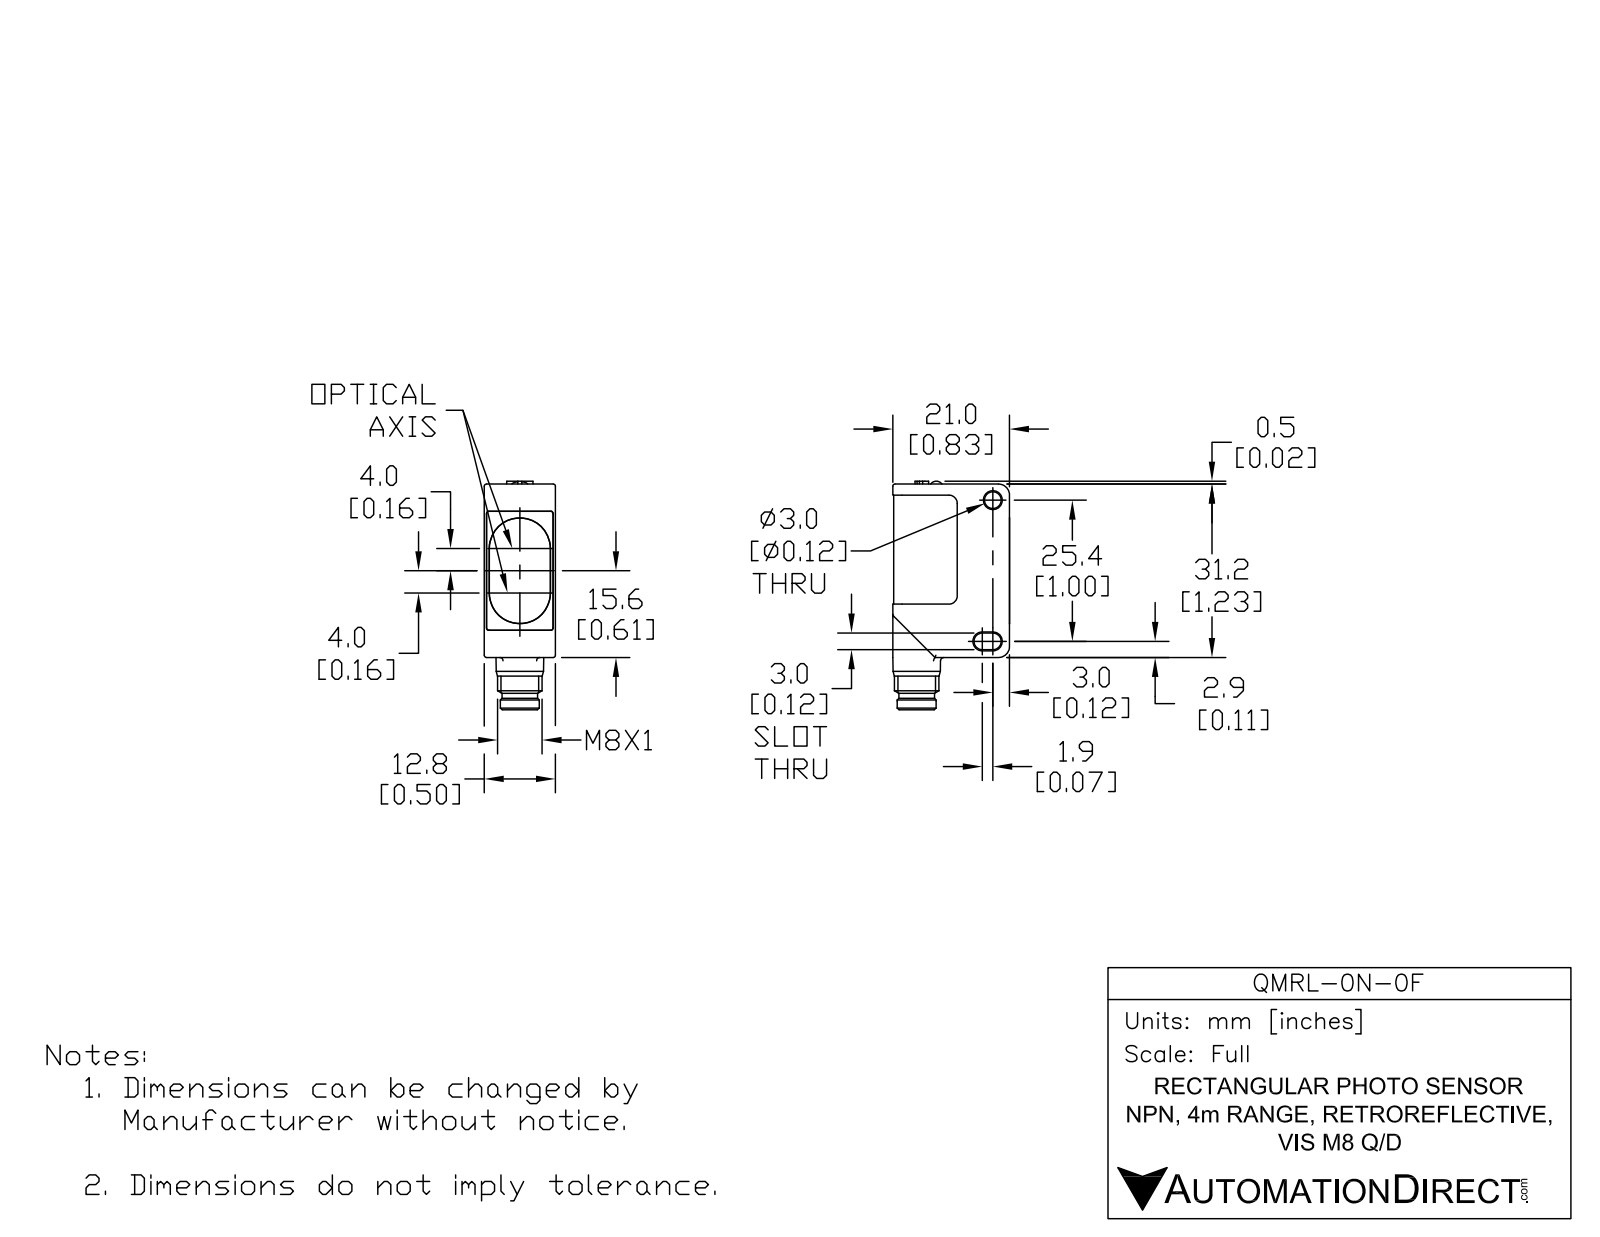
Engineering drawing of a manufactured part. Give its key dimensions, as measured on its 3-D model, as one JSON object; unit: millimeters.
{"part_name": "QMRL-0N-0F", "step_written_by": "SolidWorks 2017 (AUTOMOTIVE_DESIGN)", "units": "millimeters", "bodies": {"solids": 7, "faces": 272, "planar": 125, "cylindrical": 100, "other": 47}, "overall_size": [41.1, 21, 12.8], "volume_mm3": 7770, "surface_area_mm2": 4999, "round_holes": [[3, 3], [5.8, 1]], "round_bosses_or_shafts": [[1, 4], [3.5, 2], [8, 1], [7, 1], [6.4, 1]], "partial_cylinders_radius": [[0.4, 10], [0.5, 9], [1.5, 6], [0.6, 4], [1, 4], [0.2, 2], [1.1, 2], [1.7, 2]], "face_to_face_distances": [12.6, 0.5, 12.8, 2.8, 0.4, 12.5, 12.4, 12.2, 1.5, 18.1], "hole_center_spacings": [1, 5.2, 6.2]}
